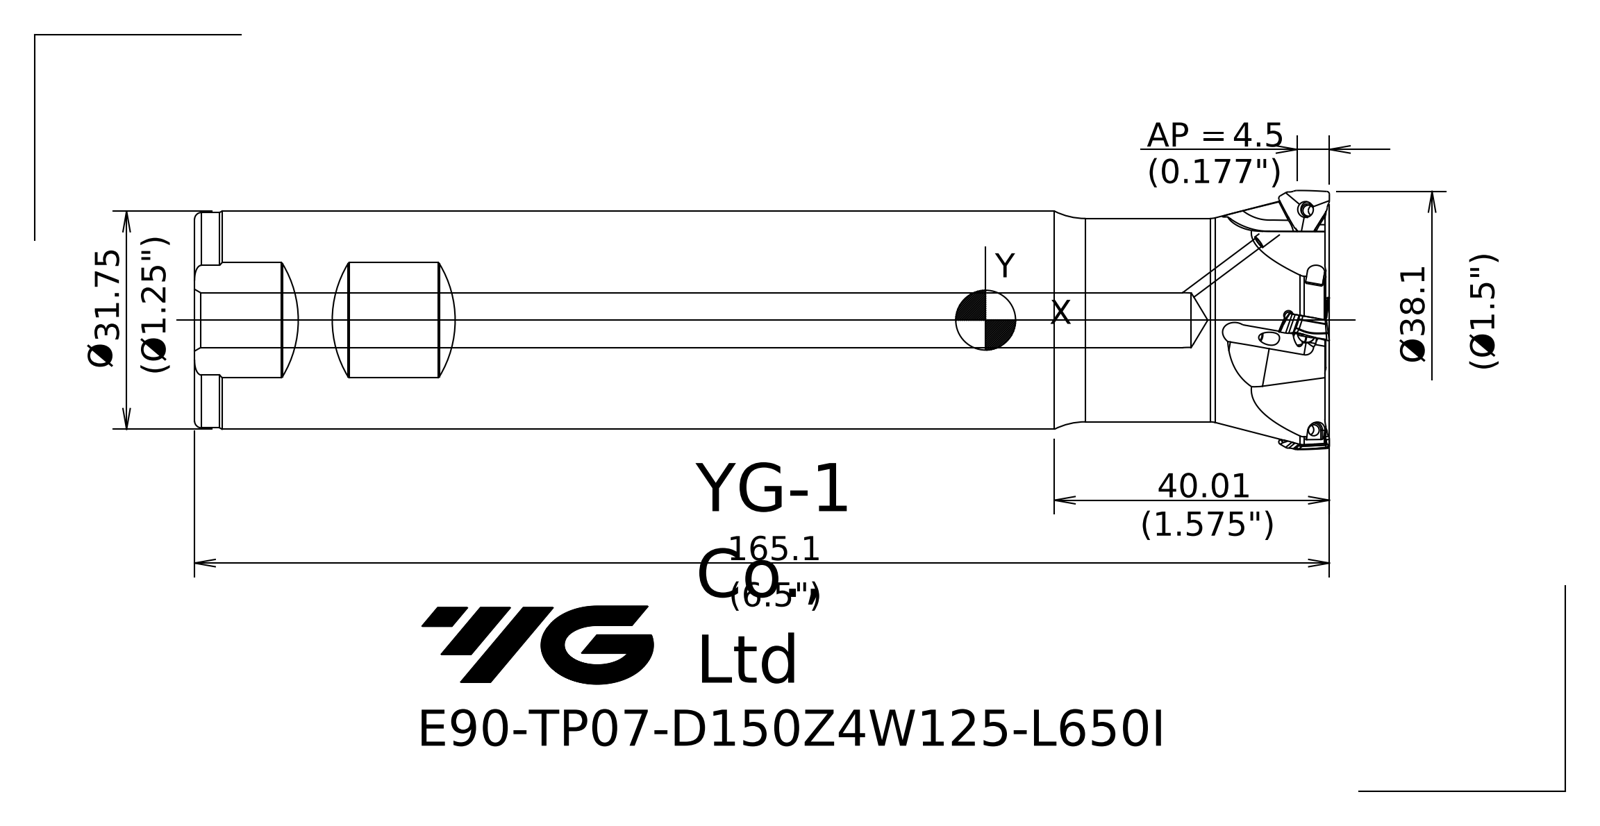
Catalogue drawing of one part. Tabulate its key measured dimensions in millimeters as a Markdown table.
| quantity | value |
| --- | --- |
| part name | 10221978745Fz3qg |
| STEP written by | SIEMENS PLM Software NX 10.0 (AP203_CONFIGURATION_CONTROLLED_3D_DESIGN_OF_MECHANICAL_PARTS_AND_ASSEMBLIES_MIM_LF) |
| units | millimeters |
| bodies | 1 solid, 51 faces (8 planar, 8 cylindrical, 35 other) |
| overall size | 165.1 × 37.98 × 37.98 |
| volume | 121 393 mm³ |
| surface area | 24 133 mm² |
| round holes (diameter × count) | 1.5 × 1, 8 × 1 |
| round bosses / shafts (diameter × count) | 31.75 × 1, 31.35 × 1, 29.6 × 1 |
| partial cylindrical surfaces (radius × count) | 0.3 × 3 |
| main face-to-face distances | 164.45, 164.6, 16.13 |
